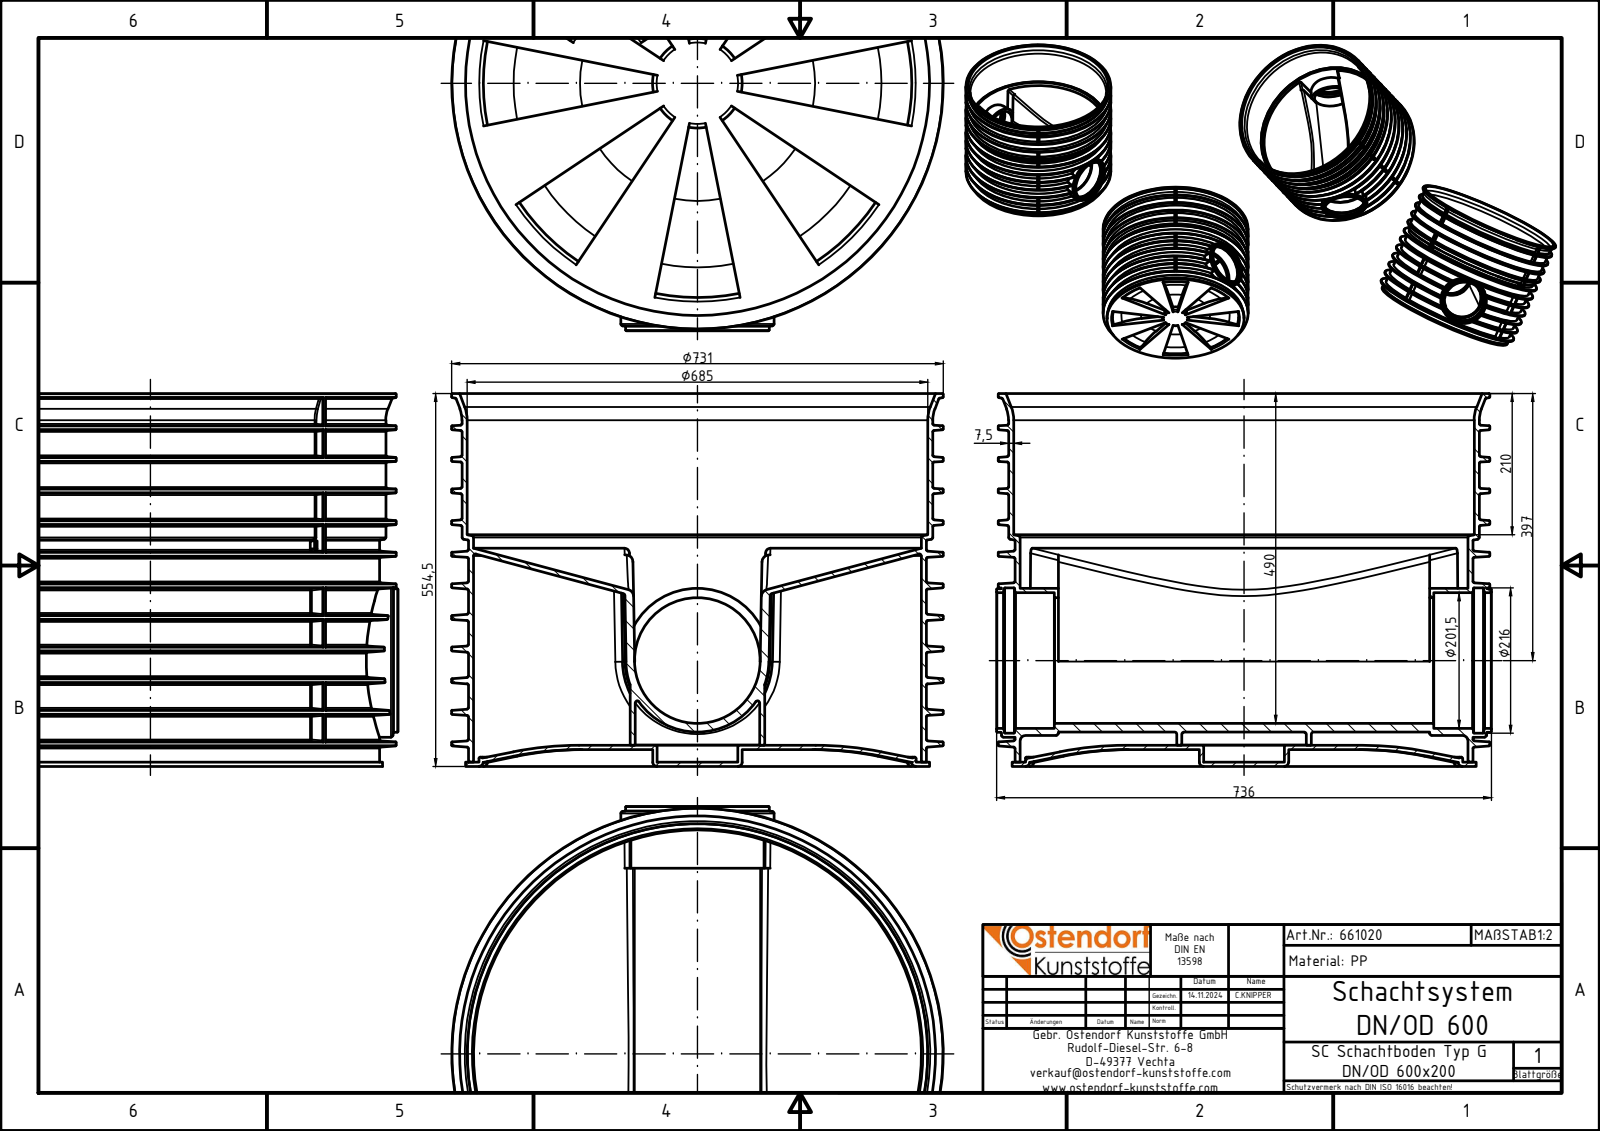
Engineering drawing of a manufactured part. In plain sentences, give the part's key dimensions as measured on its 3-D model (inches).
The part is named "661020z; 661020 Schacht DN600 Boden; 661020 Schachtboden DN600 Grundkörper". Its 3-D file was written by "Autodesk Inventor 2024 (AUTOMOTIVE_DESIGN)". It is 2 solids with 1319 faces: 142 planar, 233 cylindrical and 944 other. Overall it measures 28.976 by 28.78 by 21.831 inches. Its volume is 1 535 cubic inches and its surface area 8 460 square inches. Round holes: 1 of diameter 4.724, 1 of diameter 7.283, 1 of diameter 7.35, 1 of diameter 7.933, 1 of diameter 8.504, 1 of diameter 25.197, 1 of diameter 26.22, 1 of diameter 26.969. Round bosses or shafts: 1 of diameter 28.78, 1 of diameter 27.559, 1 of diameter 27.165, 1 of diameter 26.811, 1 of diameter 25.591, 1 of diameter 8.976, 1 of diameter 8.406, 1 of diameter 7.874. Partial cylindrical surfaces (rounded edges, fillets, slot ends): 16 of radius 0.079, 8 of radius 0.039, 4 of radius 0.118, 1 of radius 2.618, 1 of radius 4.187, 1 of radius 4.222, 1 of radius 4.384, 1 of radius 12.539. The main face-to-face distances are 0.512, 0.256, 0.984, 1.24, 0.728, 0.197, 21.831, 21.575, 20.846, 20.591.
